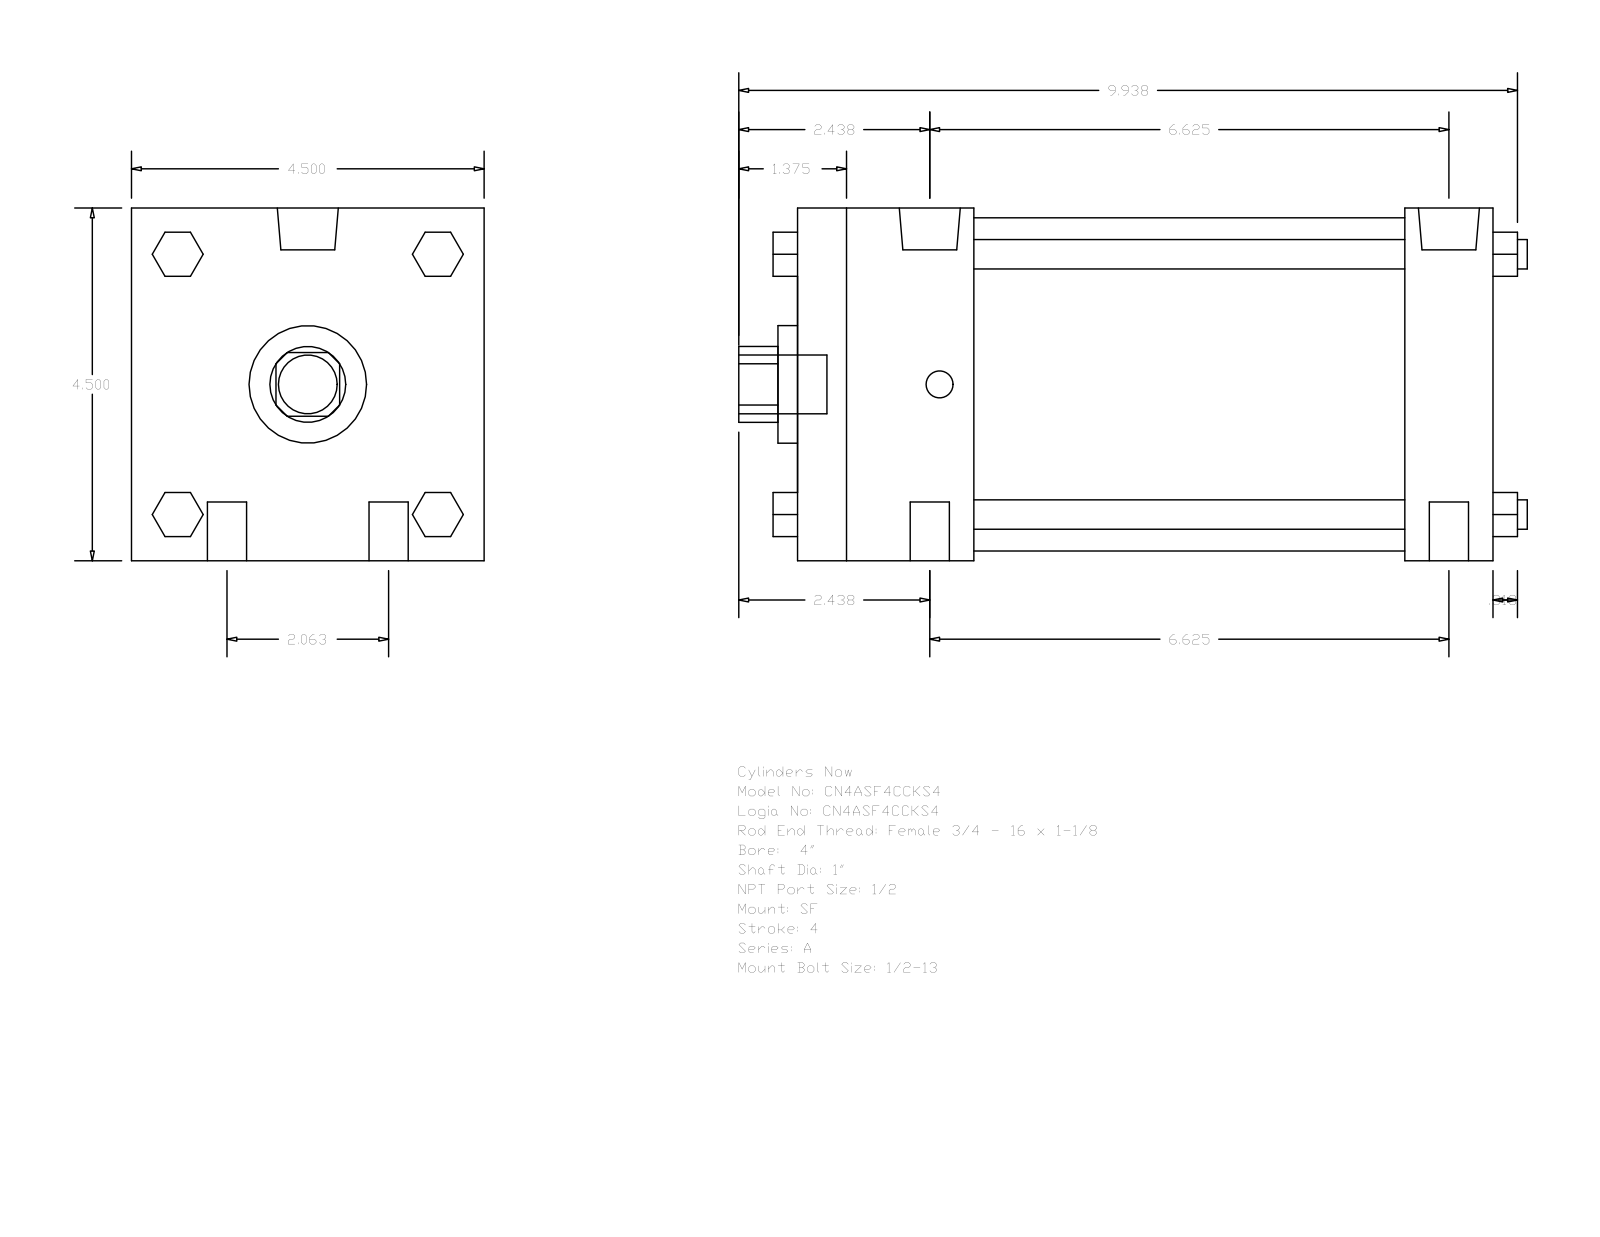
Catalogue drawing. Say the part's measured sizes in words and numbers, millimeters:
The part is named "A_SF__0400_1". Its 3-D file was written by "GSSL Pune (CONFIG_CONTROL_DESIGN)". It is 0 solids with 124 faces: 94 planar, 30 cylindrical and 0 other. Overall it measures 255.59 by 114.3 by 114.3 millimeters. Round holes: 1 of diameter 25.4, 1 of diameter 38.1, 1 of diameter 107.95. Round bosses or shafts: 4 of diameter 12.7, 4 of diameter 9.53, 2 of diameter 19.77, 2 of diameter 8.73, 1 of diameter 19.05. Partial cylindrical surfaces (rounded edges, fillets, slot ends): 1 of radius 12.29. The main face-to-face distances are 114.3, 225.42, 28.57, 196.85, 57.15, 139.7, 168.27, 14.29, 42.16, 73.03.
